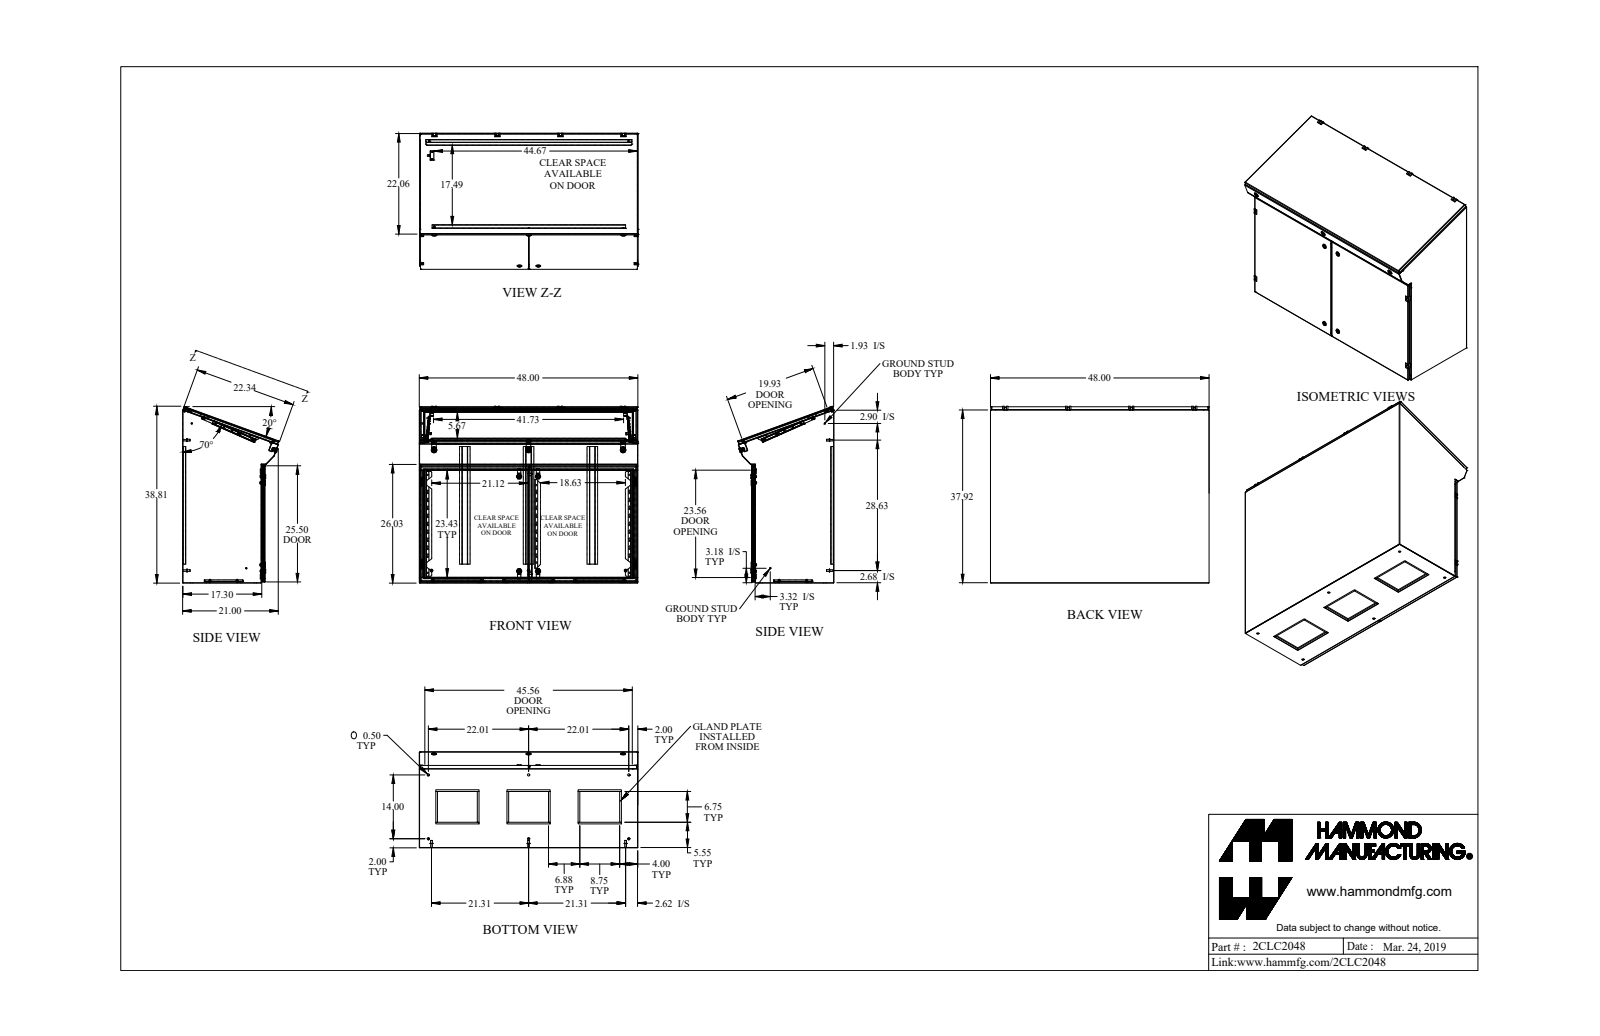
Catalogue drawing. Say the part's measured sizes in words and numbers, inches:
The part is named "2CLC2048". Its 3-D file was written by "SolidWorks 2018 (AUTOMOTIVE_DESIGN)". It is 183 solids with 3208 faces: 2234 planar, 732 cylindrical and 242 other. Overall it measures 48 by 38.742 by 21.06 inches. Its volume is 641.1 cubic inches and its surface area 16 509 square inches. Round holes: 65 of diameter 0.281, 13 of diameter 0.196, 10 of diameter 0.5, 8 of diameter 0.189, 8 of diameter 0.197, 7 of diameter 0.197, 6 of diameter 0.313, 4 of diameter 0.25, 4 of diameter 0.275, 4 of diameter 0.275, 4 of diameter 0.387, 4 of diameter 0.63. Round bosses or shafts: 19 of diameter 0.236, 17 of diameter 0.25, 14 of diameter 0.281, 8 of diameter 0.625, 8 of diameter 0.226, 6 of diameter 0.785, 6 of diameter 0.65, 6 of diameter 0.5. Partial cylindrical surfaces (rounded edges, fillets, slot ends): 61 of radius 0.036, 61 of radius 0.108, 40 of radius 0.125, 12 of radius 0.043, 12 of radius 0.116, 12 of radius 0.188, 12 of radius 0.25, 6 of radius 0.375. The main face-to-face distances are 0.072, 18.011, 18.015, 47.928, 17.939, 17.943, 0.076, 0.069, 47.856, 48. The hole center spacings are 20.75, 1.75, 3.5, 41.5, 5.25, 7, 10.5, 1.25.
